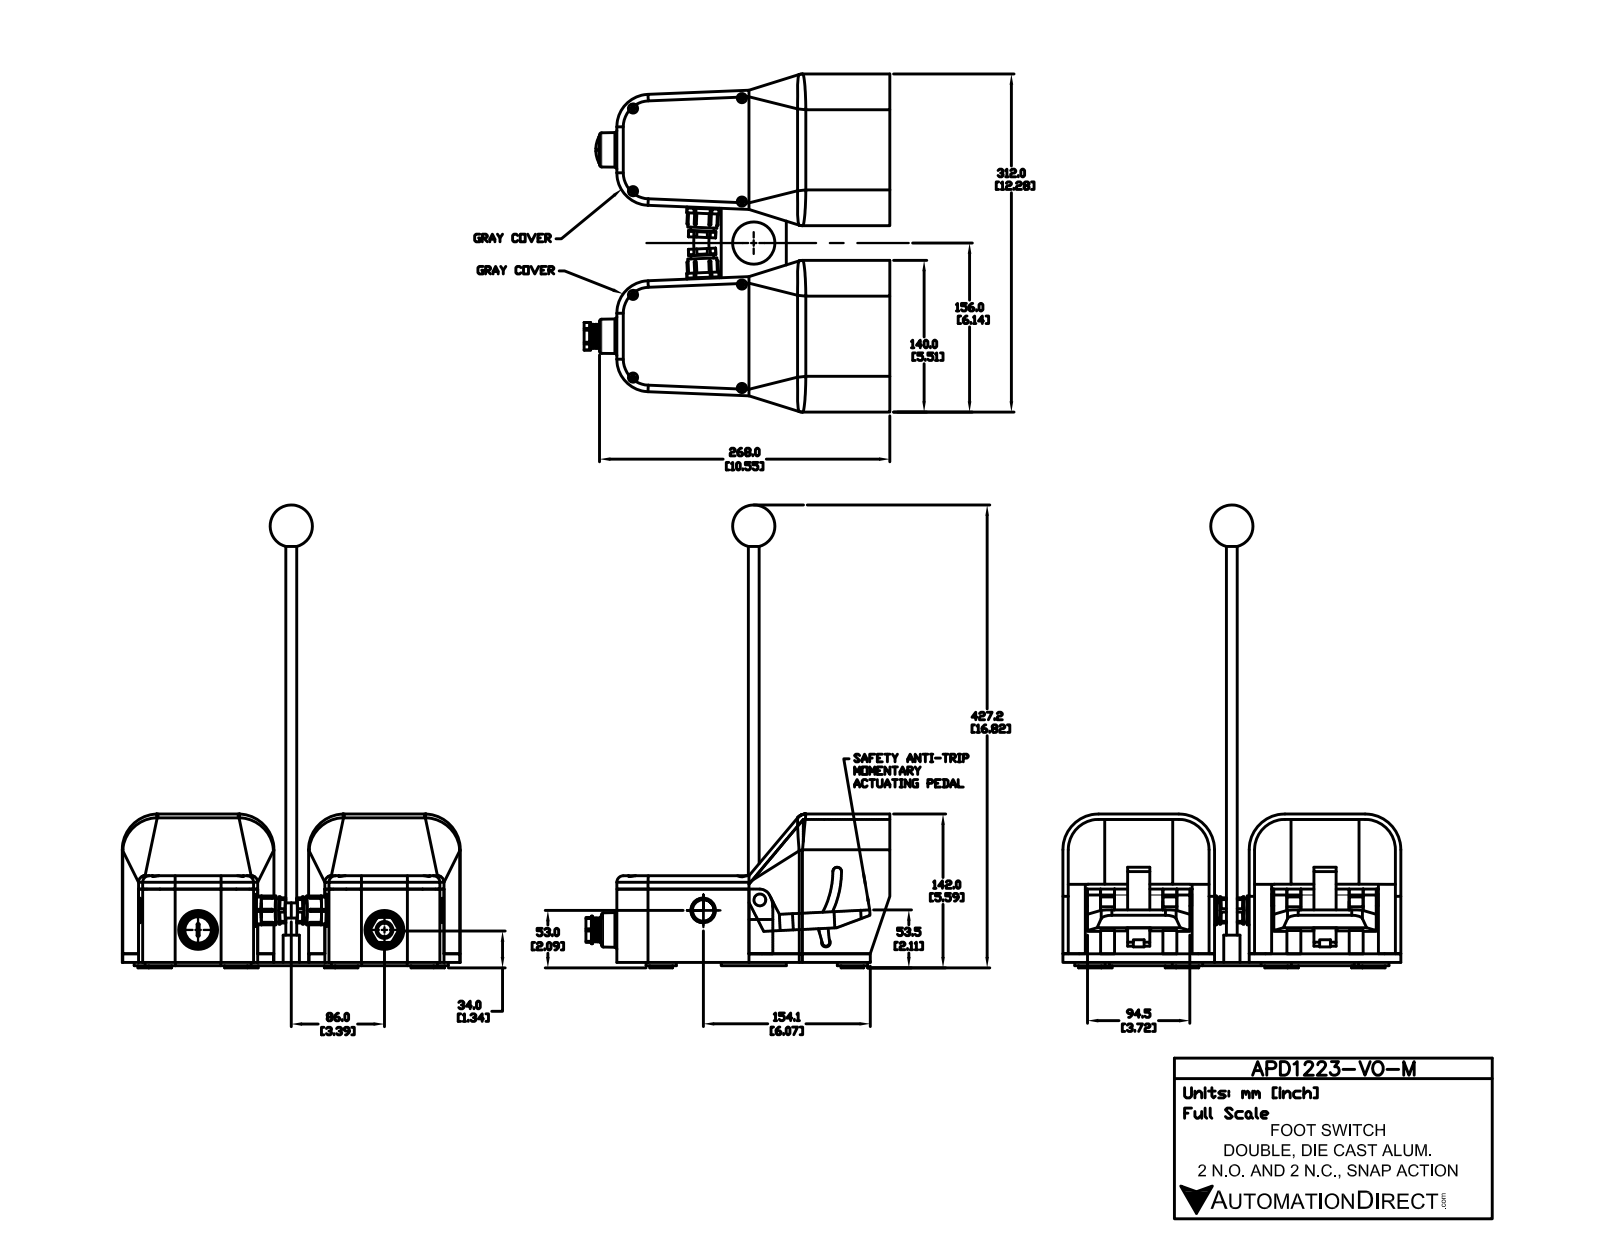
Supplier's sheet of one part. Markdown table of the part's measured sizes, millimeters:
| quantity | value |
| --- | --- |
| part name | APD1223-V0-M |
| STEP written by | SolidWorks 2017 (AUTOMOTIVE_DESIGN) |
| units | millimeters |
| bodies | 38 solids, 863 faces (512 planar, 237 cylindrical, 114 other) |
| overall size | 427.2 × 312 × 282.2 |
| volume | 3 240 000 mm³ |
| surface area | 584 800 mm² |
| round holes (diameter × count) | 8.5 × 8, 22.8 × 4, 12.6 × 1, 15.6 × 1 |
| round bosses / shafts (diameter × count) | 28 × 8, 21 × 8, 19.9 × 4, 29.7 × 2, 26.7 × 2, 25.2 × 2, 21.5 × 2, 25.5 × 1 |
| partial cylindrical surfaces (radius × count) | 1 × 34, 1.1 × 12, 10 × 11, 6 × 5, 28 × 4, 30 × 4, 33 × 4, 20 × 2 |
| main face-to-face distances | 5, 135, 172, 8, 59.6, 140, 67.7, 59.7, 67.6, 3 |
| hole center spacings | 101, 132.2, 172, 76.3, 95.5, 132.4, 191, 207.6 |
